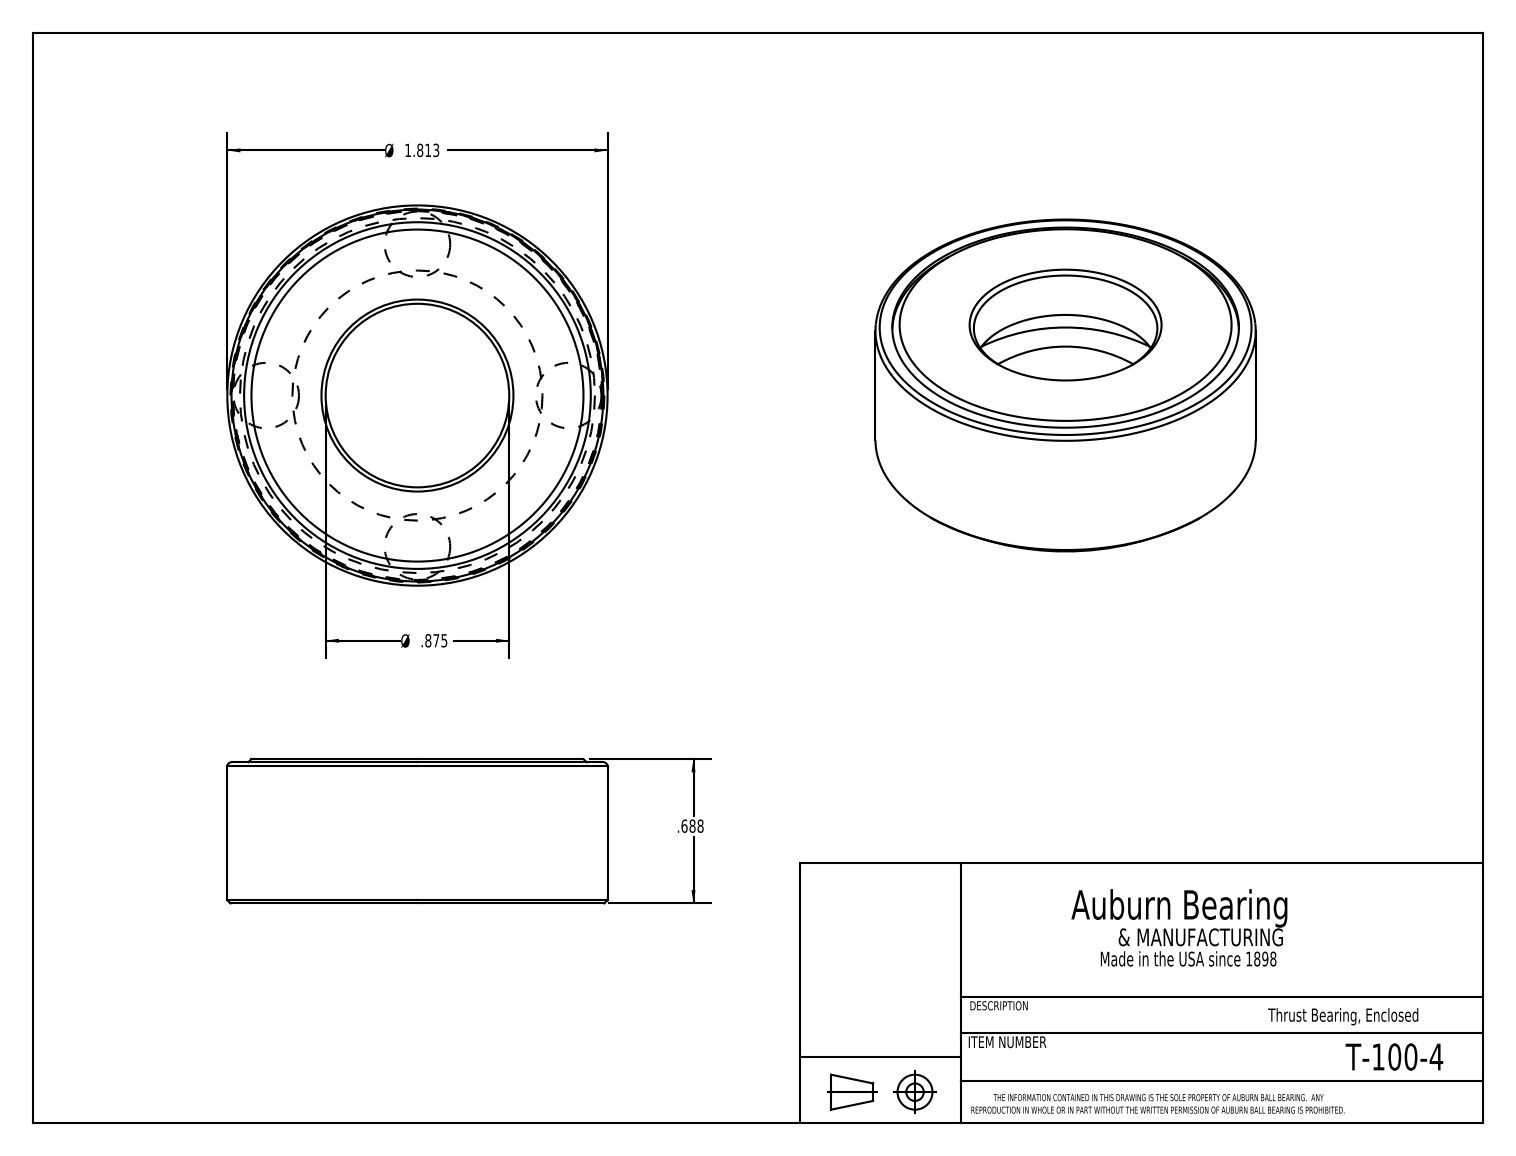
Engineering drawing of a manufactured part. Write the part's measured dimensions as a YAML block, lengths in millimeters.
part_name: "T-100-4"
step_written_by: "SolidWorks 2016 (CONFIG_CONTROL_DESIGN)"
units: millimeters
bodies: {solids: 6, faces: 28, planar: 9, cylindrical: 7, other: 12}
overall_size: [46.1, 46.1, 17.5]
volume: 15500
surface_area: 11850
round_holes:
  - {diameter: 22.2, count: 1}
  - {diameter: 42, count: 1}
  - {diameter: 45, count: 1}
round_bosses_or_shafts:
  - {diameter: 46.1, count: 1}
  - {diameter: 44.7, count: 1}
face_to_face_distances: [6.4, 11.1, 17.4, 4.7, 16.6, 10.2, 5.5, 0.9, 17.1, 10.7]
